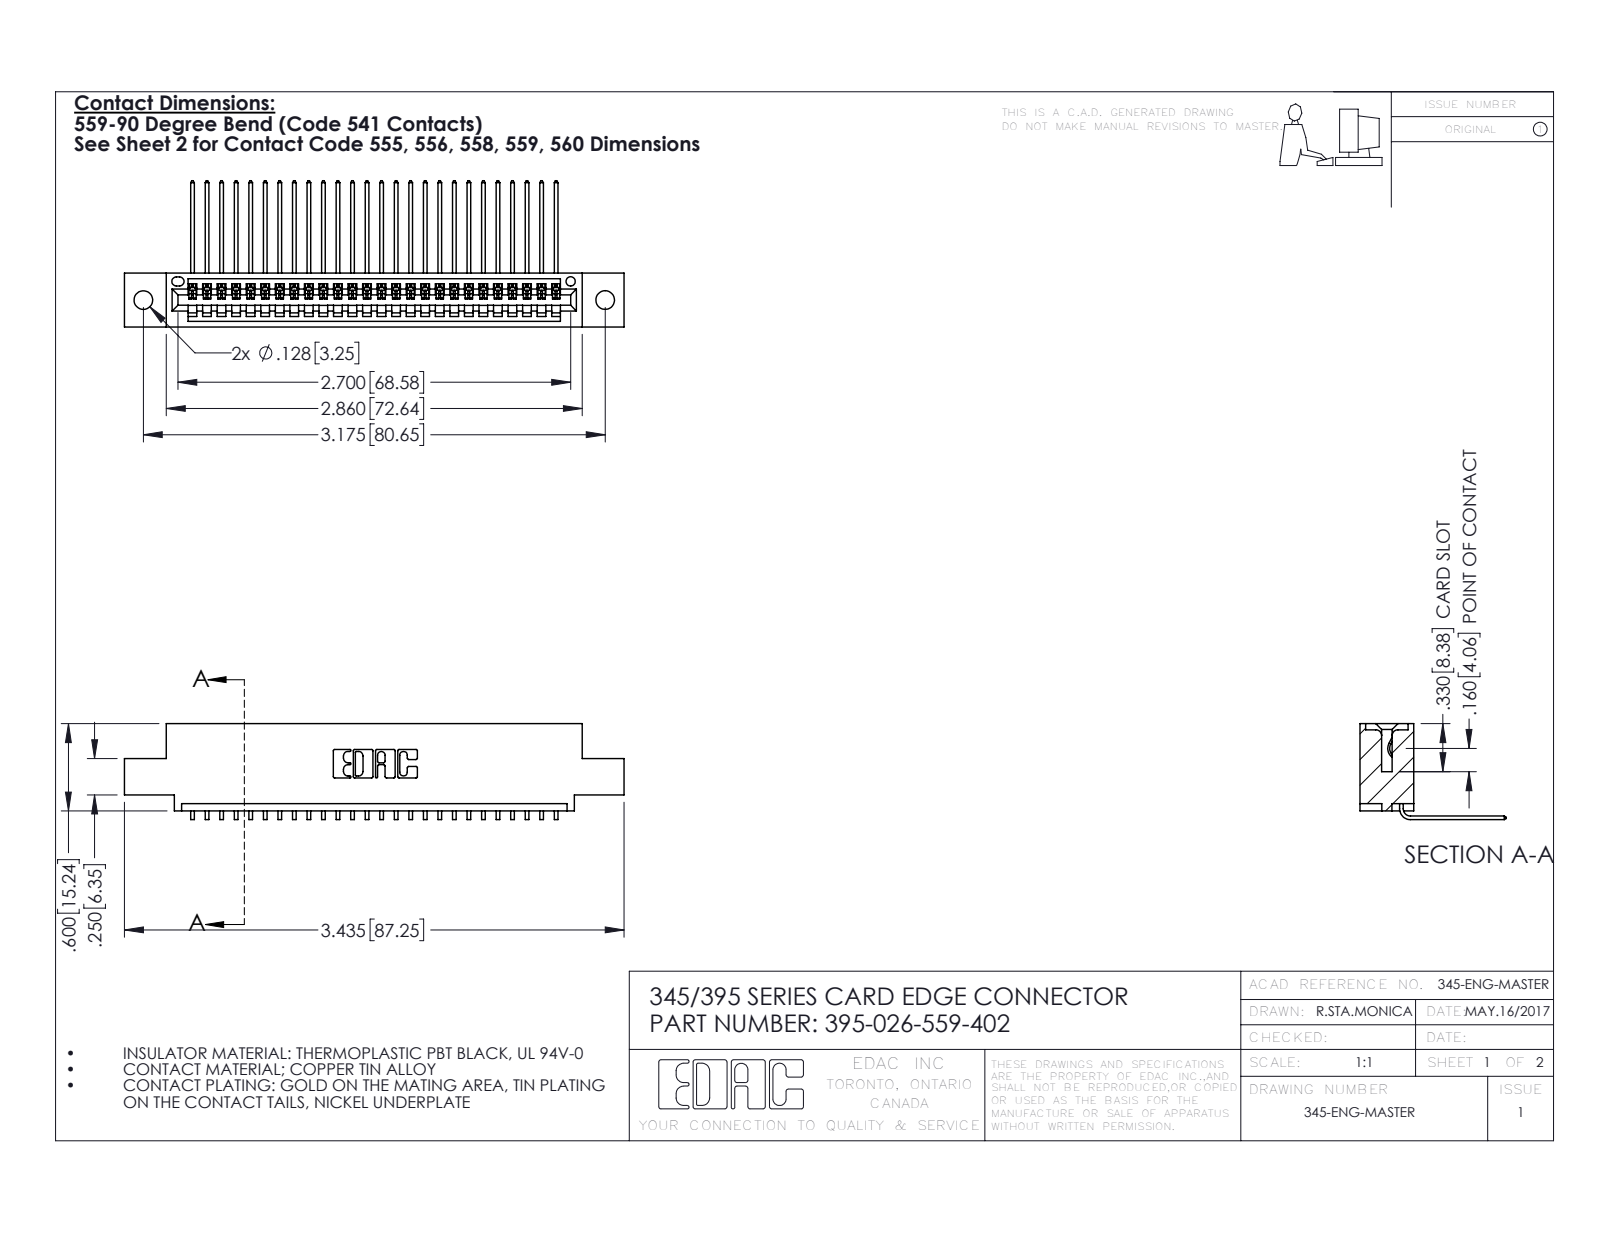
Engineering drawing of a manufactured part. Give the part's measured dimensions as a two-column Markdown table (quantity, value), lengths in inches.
| quantity | value |
| --- | --- |
| part name | 345-292-001_558 559 Tail - 1; 395-026-559-402; 345 Part_0.110 Offset - 0.128 Dia |
| STEP written by | SolidWorks 2016 (CONFIG_CONTROL_DESIGN) |
| units | inches |
| bodies | 27 solids, 1690 faces (1176 planar, 514 cylindrical, 0 other) |
| overall size | 3.435 × 1.005 × 0.659 |
| volume | 0.496 in³ |
| surface area | 16.91 in² |
| round holes (diameter × count) | 0.128 × 2, 0.064 × 1 |
| partial cylindrical surfaces (radius × count) | 0.006 × 52, 0.01 × 22, 0.007 × 6, 0.031 × 6, 0.026 × 3, 0.031 × 2, 0.04 × 2, 0.014 × 1 |
| main face-to-face distances | 0.072, 0.298, 0.37, 0.2, 0.098, 0.272, 0.025, 0.225, 0.149, 0.072 |
| hole center spacings | 0.27, 2.94, 3.175 |
